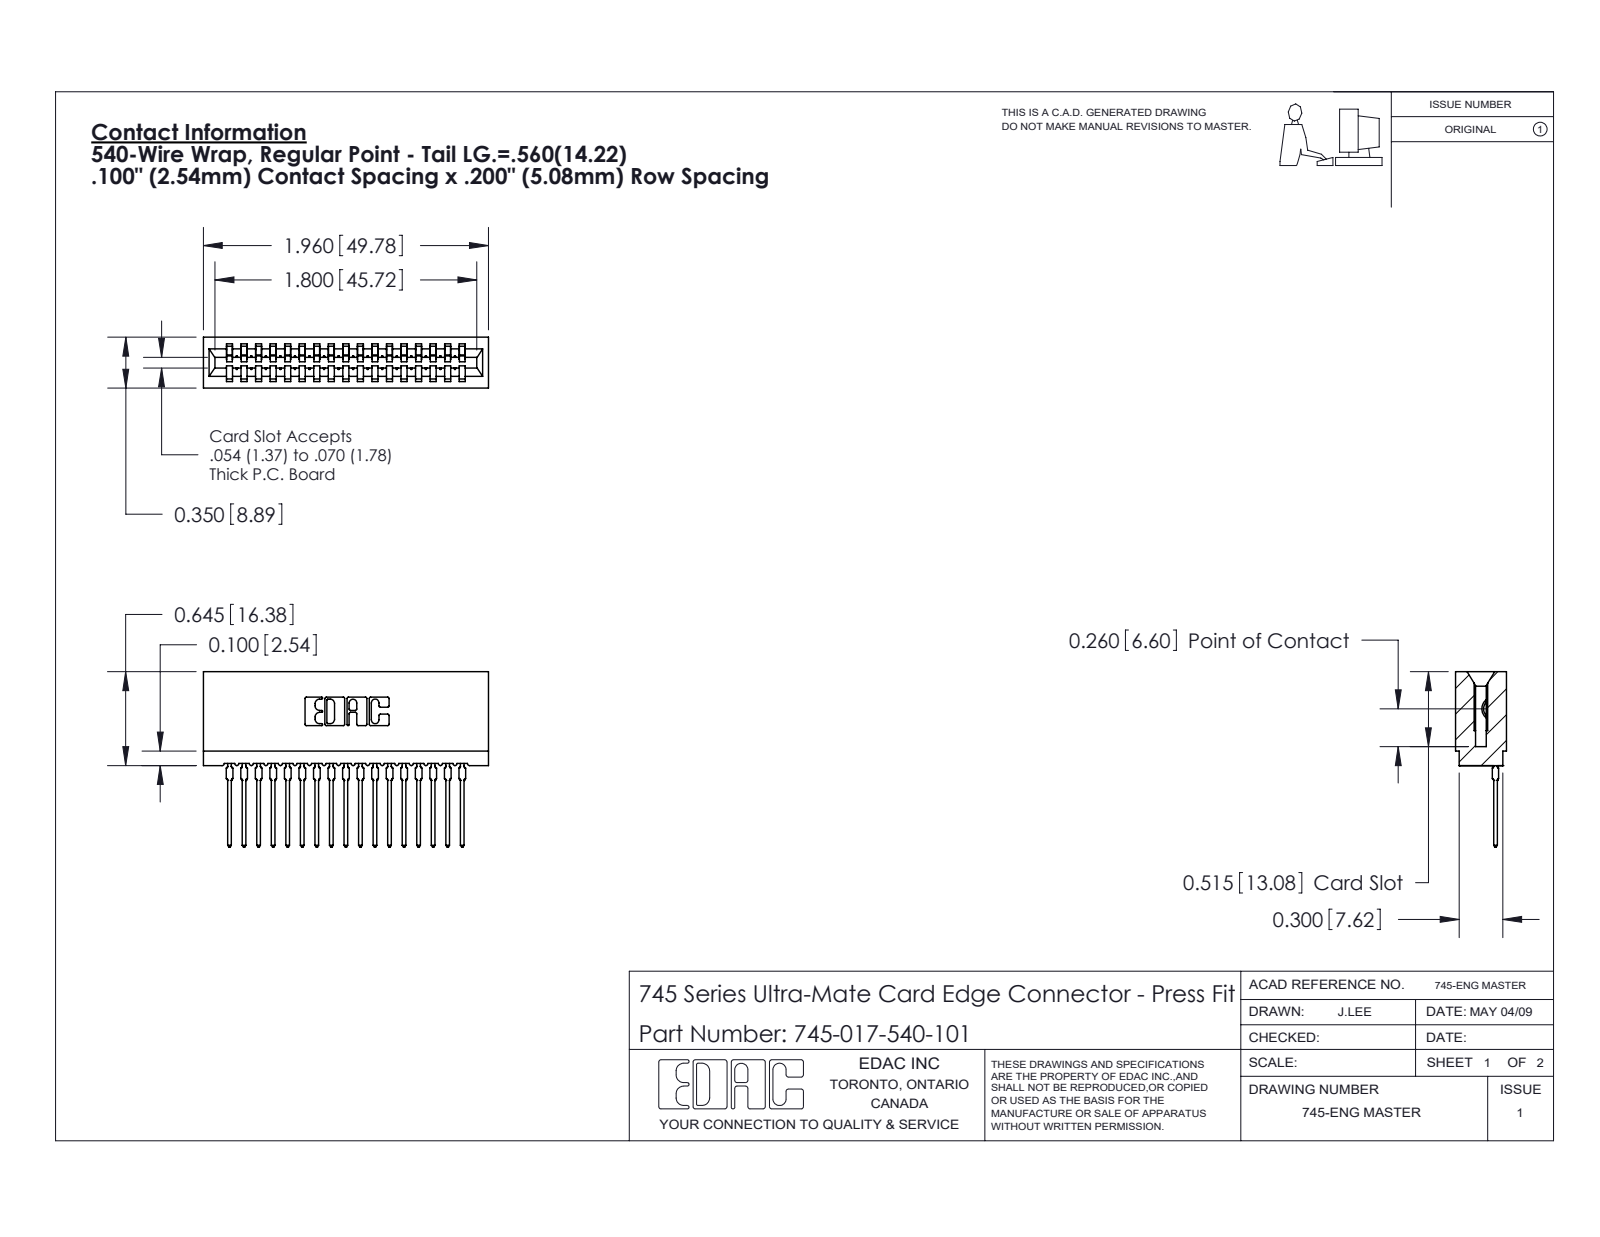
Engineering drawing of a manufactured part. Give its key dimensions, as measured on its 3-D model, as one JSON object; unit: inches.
{"part_name": "745-292-001_540; 745 Part_Insulator Option - 01; 745-017-540-101", "step_written_by": "SolidWorks 2020 (CONFIG_CONTROL_DESIGN)", "units": "inches", "bodies": {"solids": 18, "faces": 1999, "planar": 1194, "cylindrical": 363, "other": 442}, "overall_size": [1.96, 1.206, 0.35], "volume_in3": 0.276, "surface_area_in2": 12.57, "partial_cylinders_radius": [[0.015, 34], [0.021, 34], [0.01, 22], [0.007, 6], [0.031, 6], [0.005, 4], [0.011, 4], [0.026, 3]], "face_to_face_distances": [0.1, 0.2, 0.3, 0.4, 0.5, 0.6, 0.35, 0.7, 0.8, 0.138]}
